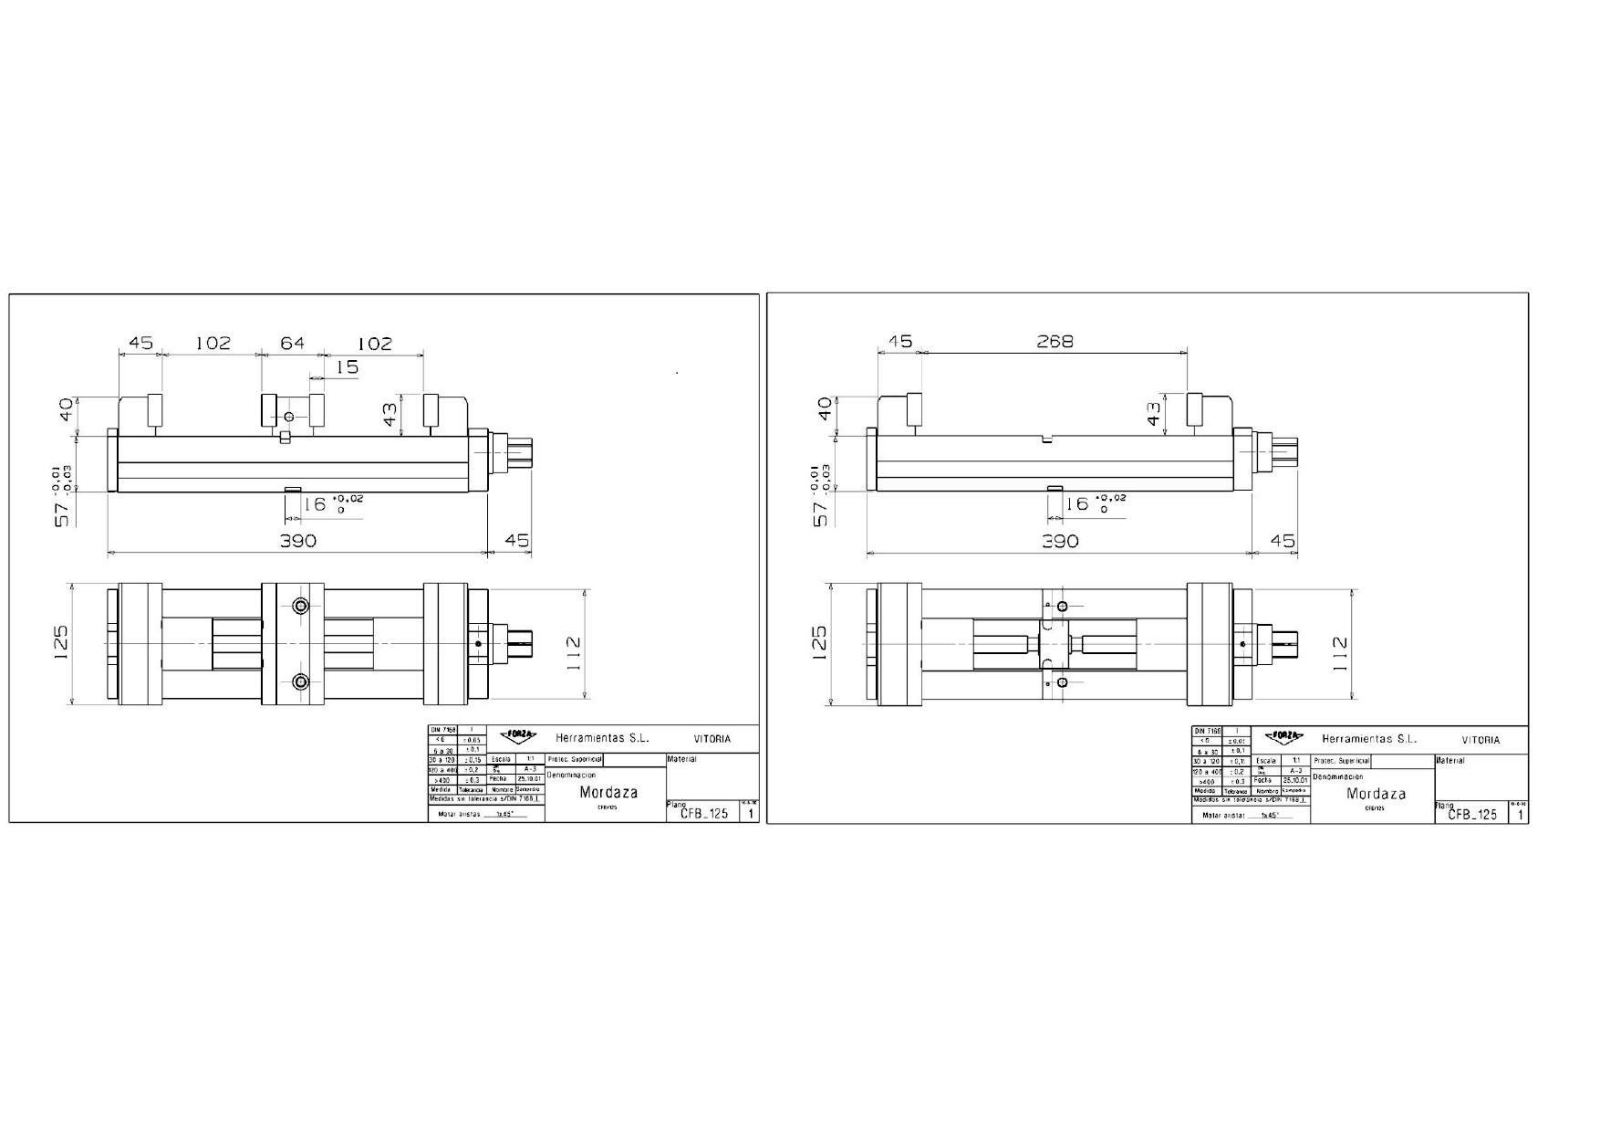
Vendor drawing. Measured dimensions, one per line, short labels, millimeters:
name: CFB_125_Mordaza
written by: SIEMENS PLM Software NX 9.0 (CONFIG_CONTROL_DESIGN)
unit: mm
bodies: 33 solids, 635 faces (417 planar, 139 cylindrical, 79 other)
size: 435 × 125 × 100
volume: 2 578 000 mm³; area: 463 545 mm²
holes: 7× ⌀5.19, 5× ⌀8.78, 4× ⌀10.5, 3× ⌀6.1, 3× ⌀11, 2× ⌀3.43, 2× ⌀4.35, 2× ⌀8.1, 2× ⌀16.5, 2× ⌀17, 1× ⌀2.46, 1× ⌀16
bosses: 5× ⌀10, 5× ⌀5.79, 2× ⌀15, 1× ⌀42, 1× ⌀40, 1× ⌀30, 1× ⌀28, 1× ⌀24
rounds: 2× R5, 2× R8
face distances: 31, 20, 57, 25, 37, 1, 166, 15, 30, 58
hole spacings: 40, 151.34, 8.94, 10, 16.12, 31.05, 31.24, 39.12
